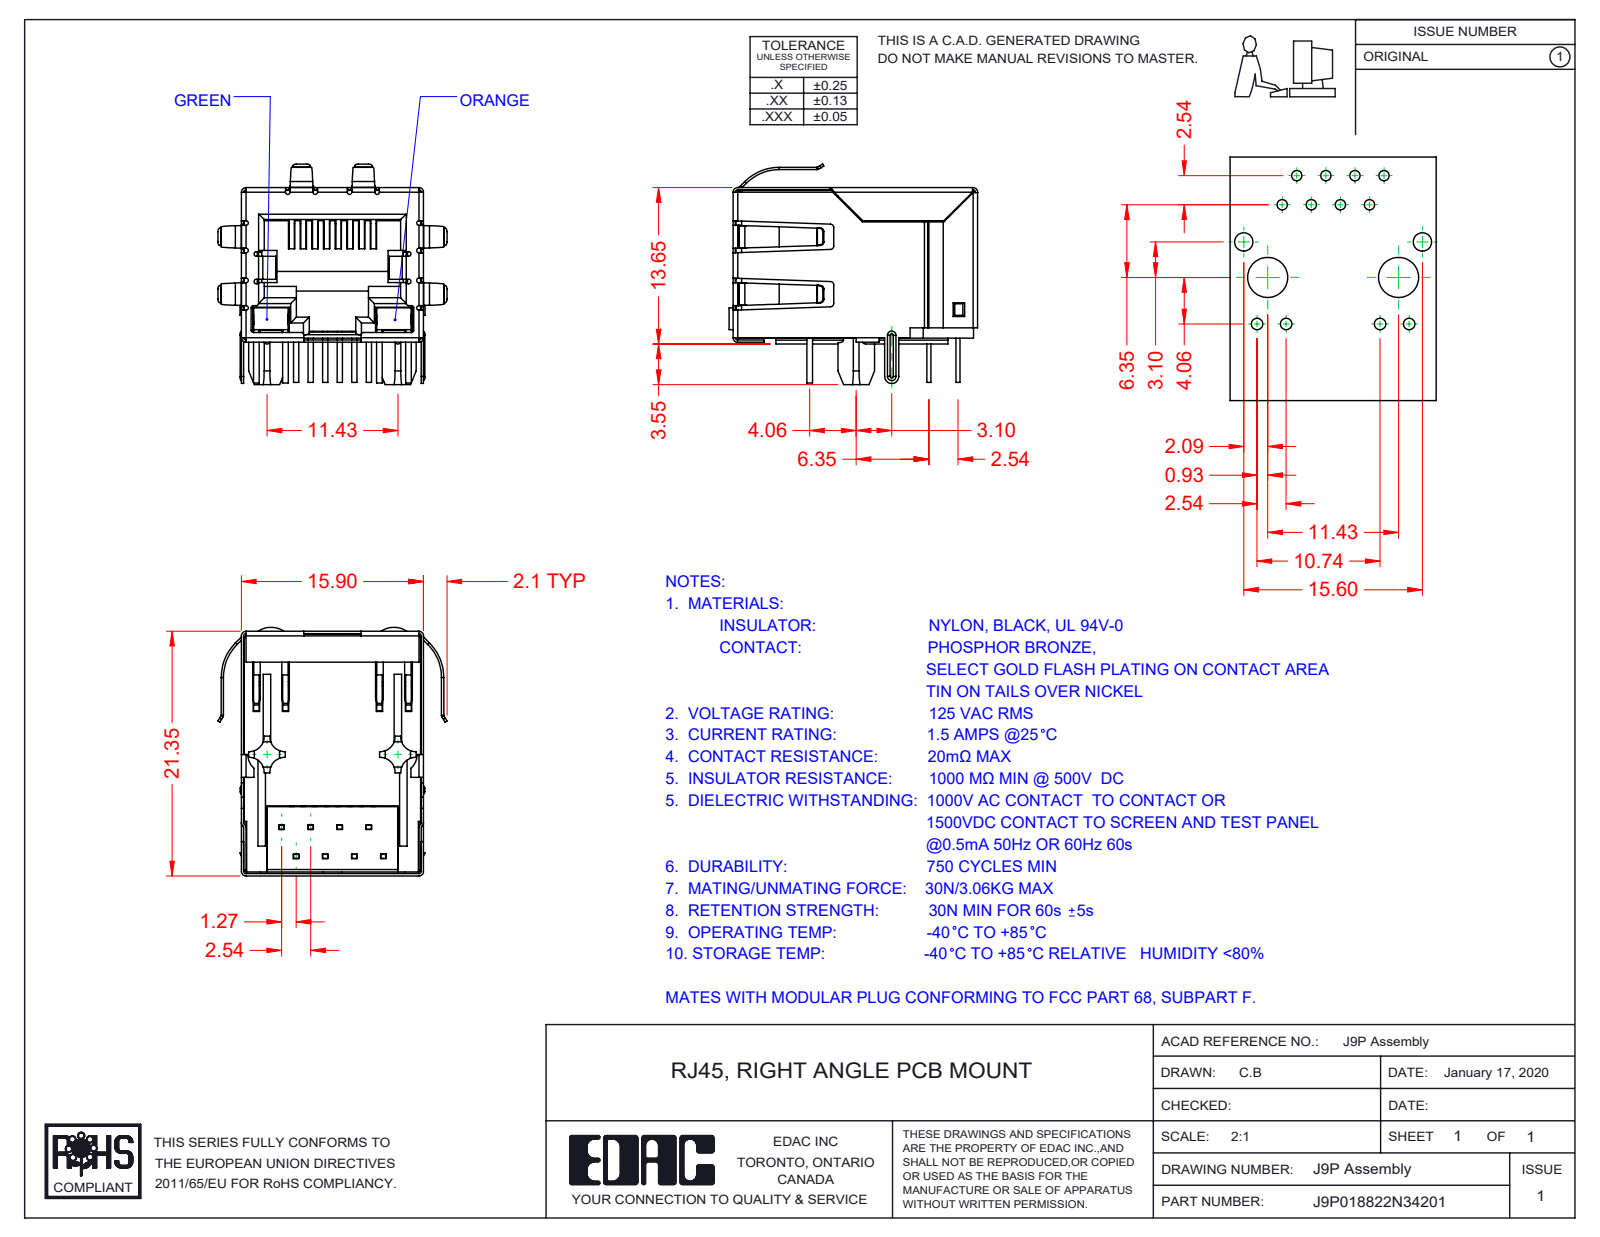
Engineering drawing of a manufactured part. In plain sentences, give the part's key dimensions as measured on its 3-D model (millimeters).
The part is named "J9P018822N34202; 9P-LED LED RH_4-Orange; 9P-LED LED LH_3-Green; 9P-LED Contact Lock (+4 more)". Its 3-D file was written by "SolidWorks 2016 (CONFIG_CONTROL_DESIGN)". It is 13 solids with 1472 faces: 1042 planar, 336 cylindrical and 94 other. Overall it measures 21.7 by 20 by 19.25 millimeters. Its volume is 2 687 cubic millimeters and its surface area 7 515 square millimeters. Partial cylindrical surfaces (rounded edges, fillets, slot ends): 39 of radius 0.2, 22 of radius 0.5, 20 of radius 0.3, 16 of radius 0.4, 8 of radius 1.3, 5 of radius 0.23, 4 of radius 0.11, 4 of radius 0.31. The main face-to-face distances are 15.45, 15.7, 15.65, 0.35, 0.54, 15.5, 12.36, 0.6, 1.4, 0.59.
